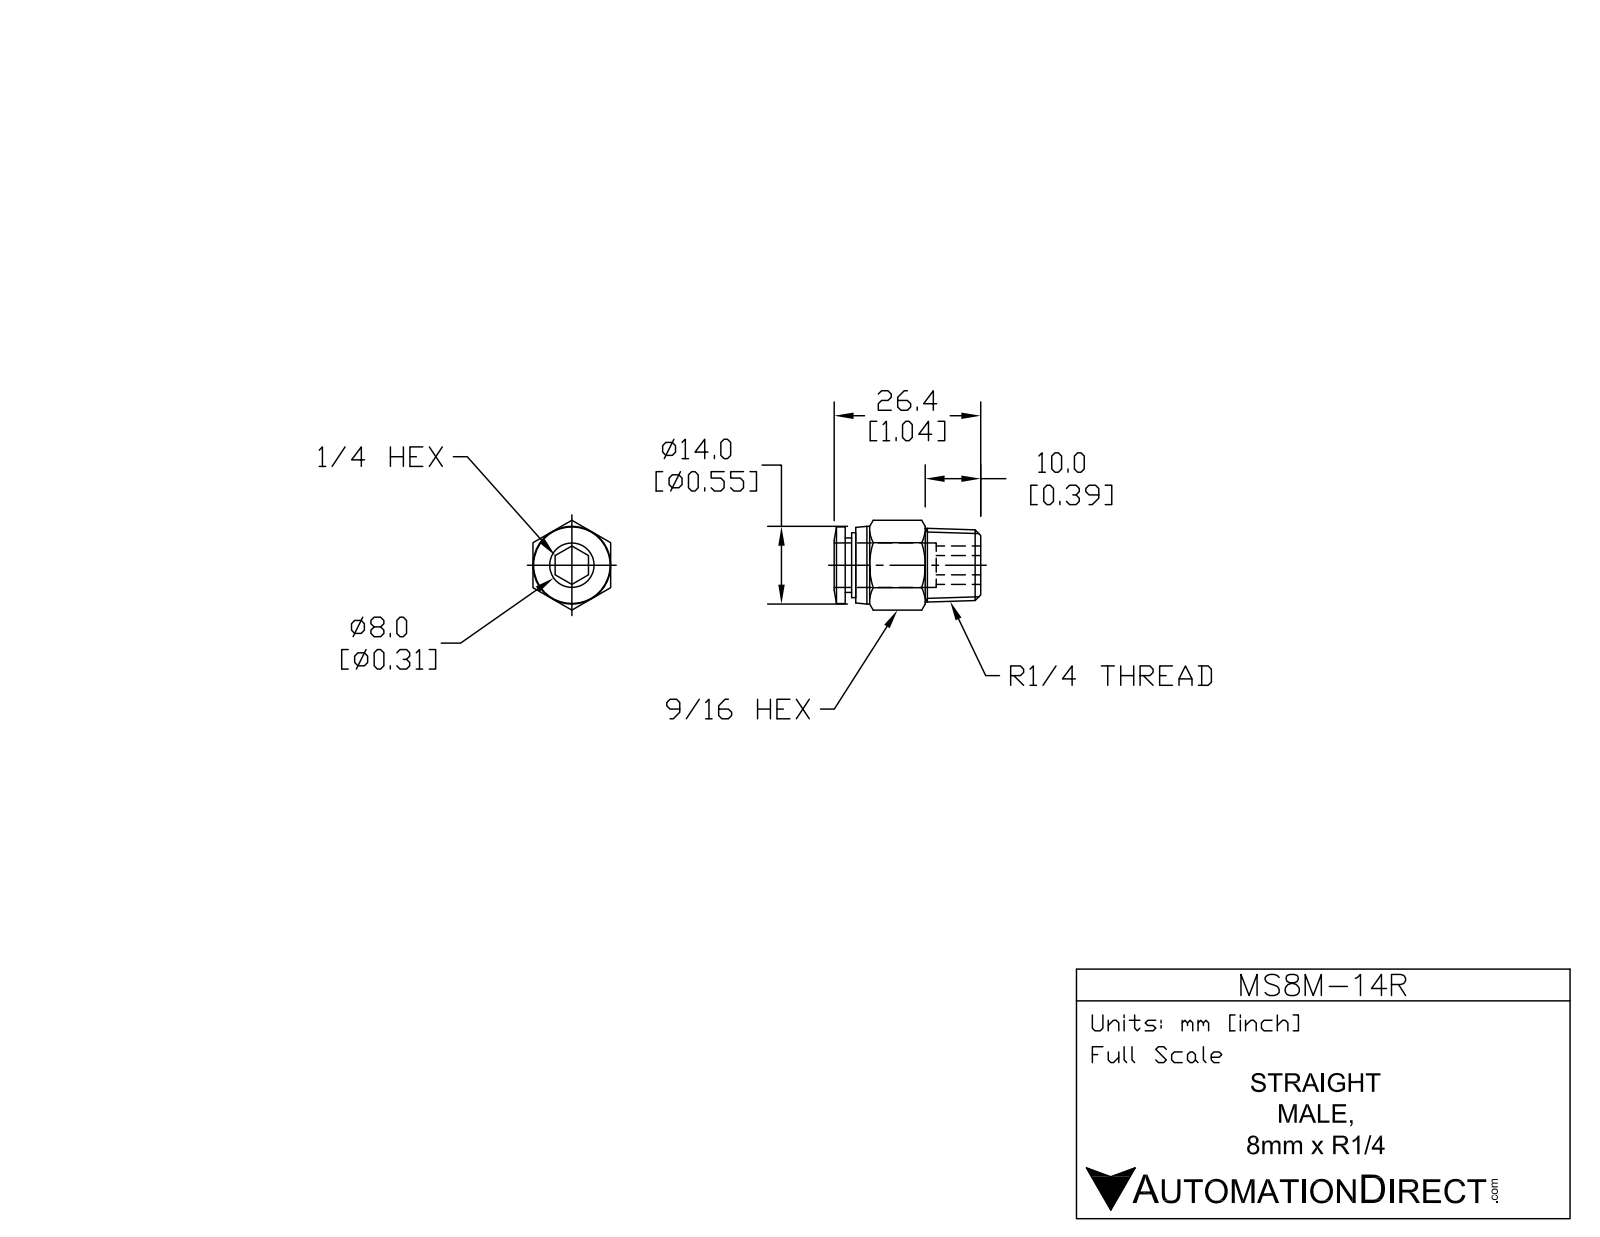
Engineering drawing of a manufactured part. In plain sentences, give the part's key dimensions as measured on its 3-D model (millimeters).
The part is named "MS8M-14R". Its 3-D file was written by "SolidWorks 2015 (AUTOMOTIVE_DESIGN)". It is 1 solid with 48 faces: 13 planar, 12 cylindrical and 23 other. Overall it measures 26.4 by 16.2 by 14 millimeters. Its volume is 2 520 cubic millimeters and its surface area 2 138 square millimeters. Round holes: 1 of diameter 7, 1 of diameter 8.3. Round bosses or shafts: 1 of diameter 14, 1 of diameter 13.8, 1 of diameter 11.7, 1 of diameter 9.8. The main face-to-face distances are 14, 24.4, 22.5, 1.9, 23.2, 0.8, 1.1, 16.4, 2, 8.
